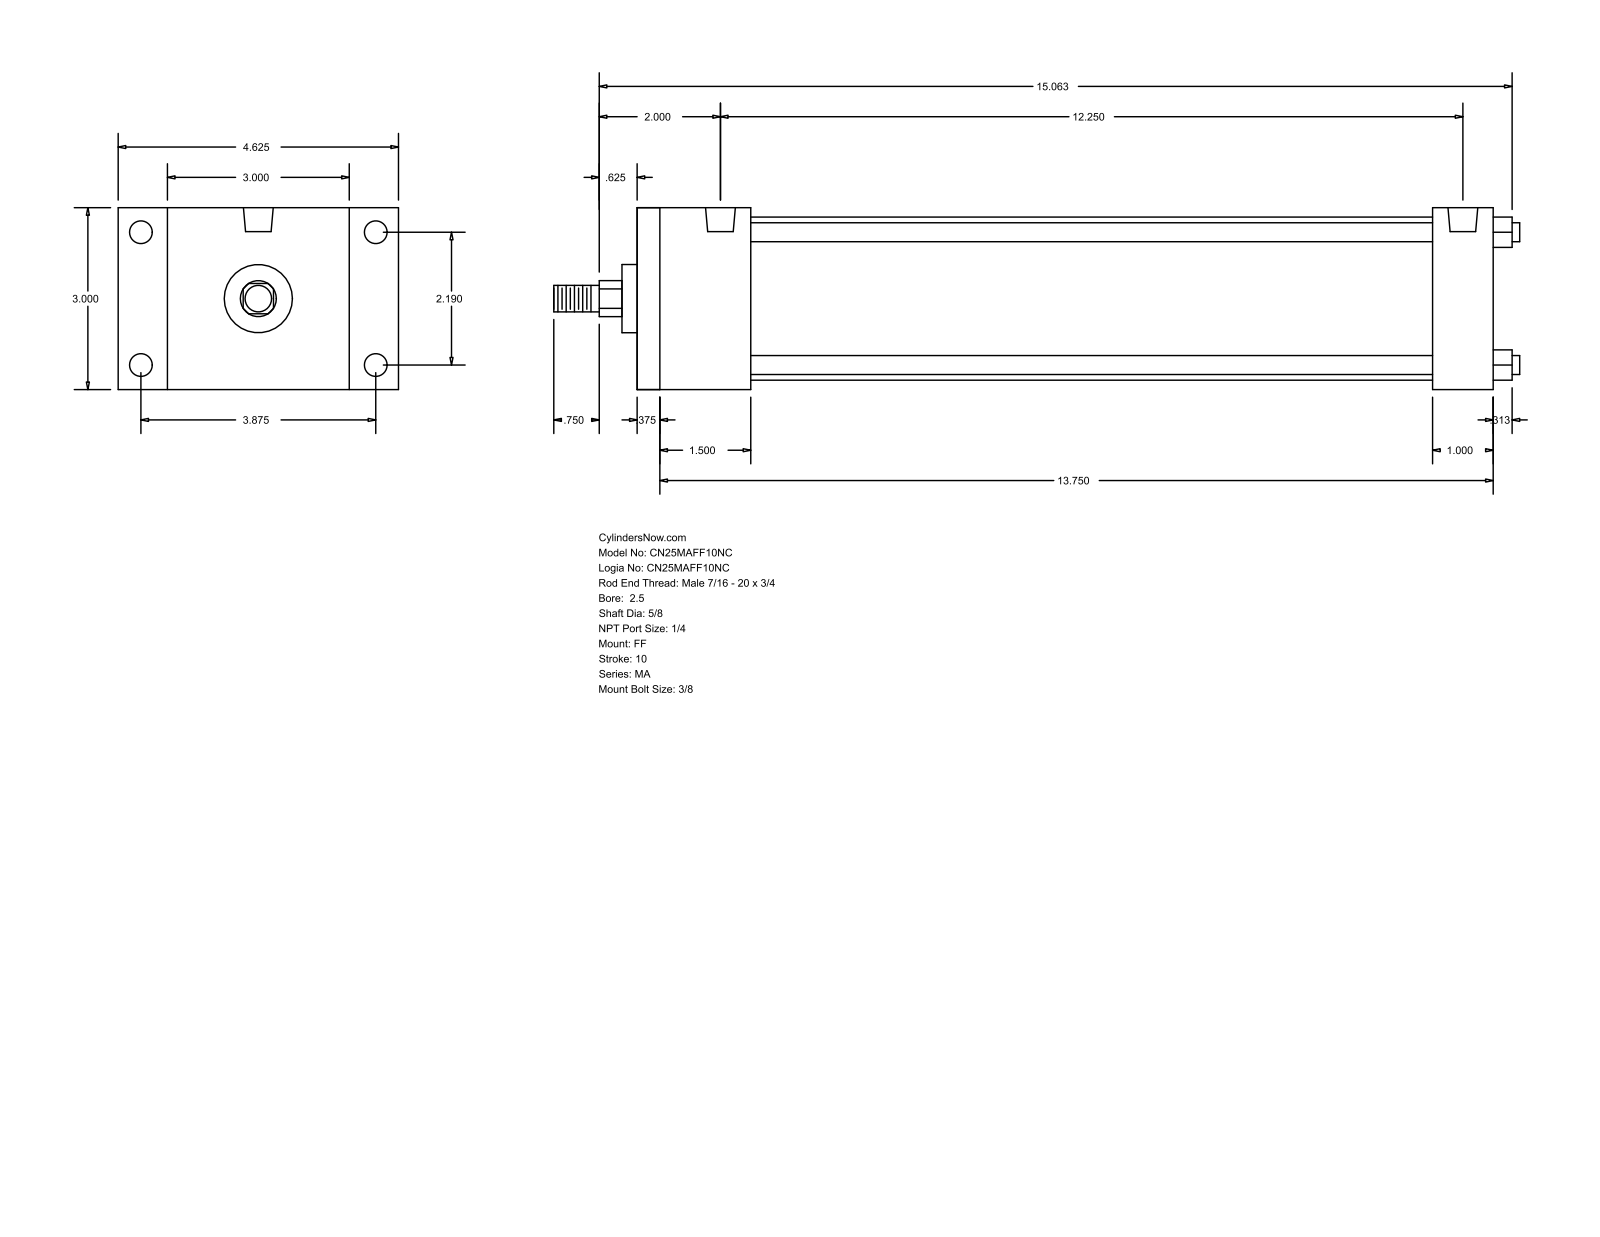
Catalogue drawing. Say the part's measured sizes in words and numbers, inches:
The part is named "MA_FF__0250_0.625". Its 3-D file was written by "GSSL Pune (CONFIG_CONTROL_DESIGN)". It is 0 solids with 92 faces: 64 planar, 28 cylindrical and 0 other. Overall it measures 15.937 by 4.625 by 3 inches. Round holes: 4 of diameter 0.313, 4 of diameter 0.375, 2 of diameter 0.492. Round bosses or shafts: 4 of diameter 0.313, 1 of diameter 2.69, 1 of diameter 1.125, 1 of diameter 0.625, 1 of diameter 0.437. Partial cylindrical surfaces (rounded edges, fillets, slot ends): 1 of radius 0.297. The main face-to-face distances are 3, 14.125, 13.75, 0.375, 1, 1.875, 13.125, 1.5, 12.75, 11.25. The hole center spacings are 2.19, 3.875, 4.451, 12.25.
